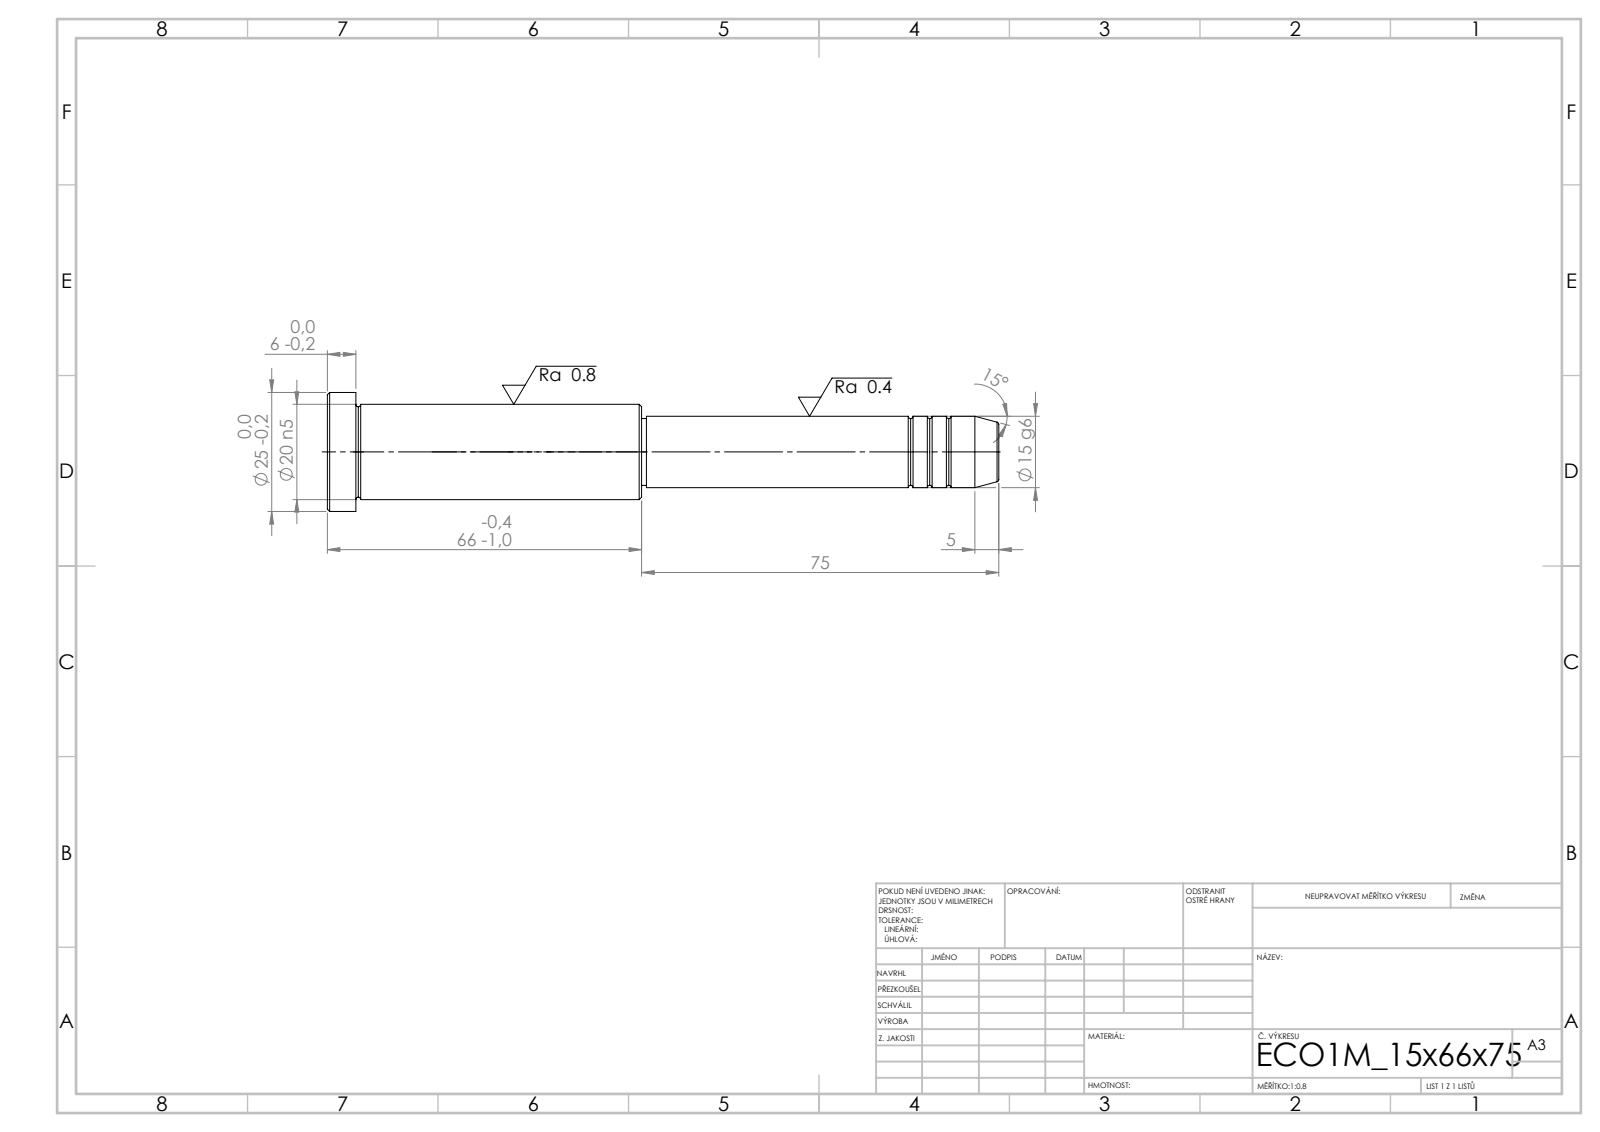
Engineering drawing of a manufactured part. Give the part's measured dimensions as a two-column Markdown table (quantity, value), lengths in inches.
| quantity | value |
| --- | --- |
| STEP written by | SolidWorks 2019 (CONFIG_CONTROL_DESIGN) |
| units | inches |
| bodies | 1 solid, 43 faces (5 planar, 14 cylindrical, 24 other) |
| overall size | 5.551 × 0.984 × 0.984 |
| volume | 2.122 in³ |
| surface area | 13.62 in² |
| round bosses / shafts (diameter × count) | 0.984 × 1, 0.787 × 1, 0.591 × 1, 0.551 × 1 |
| main face-to-face distances | 0.236, 2.362, 2.598, 2.953, 5.315, 5.551, 2.913, 0.039, 2.402, 2.638 |
